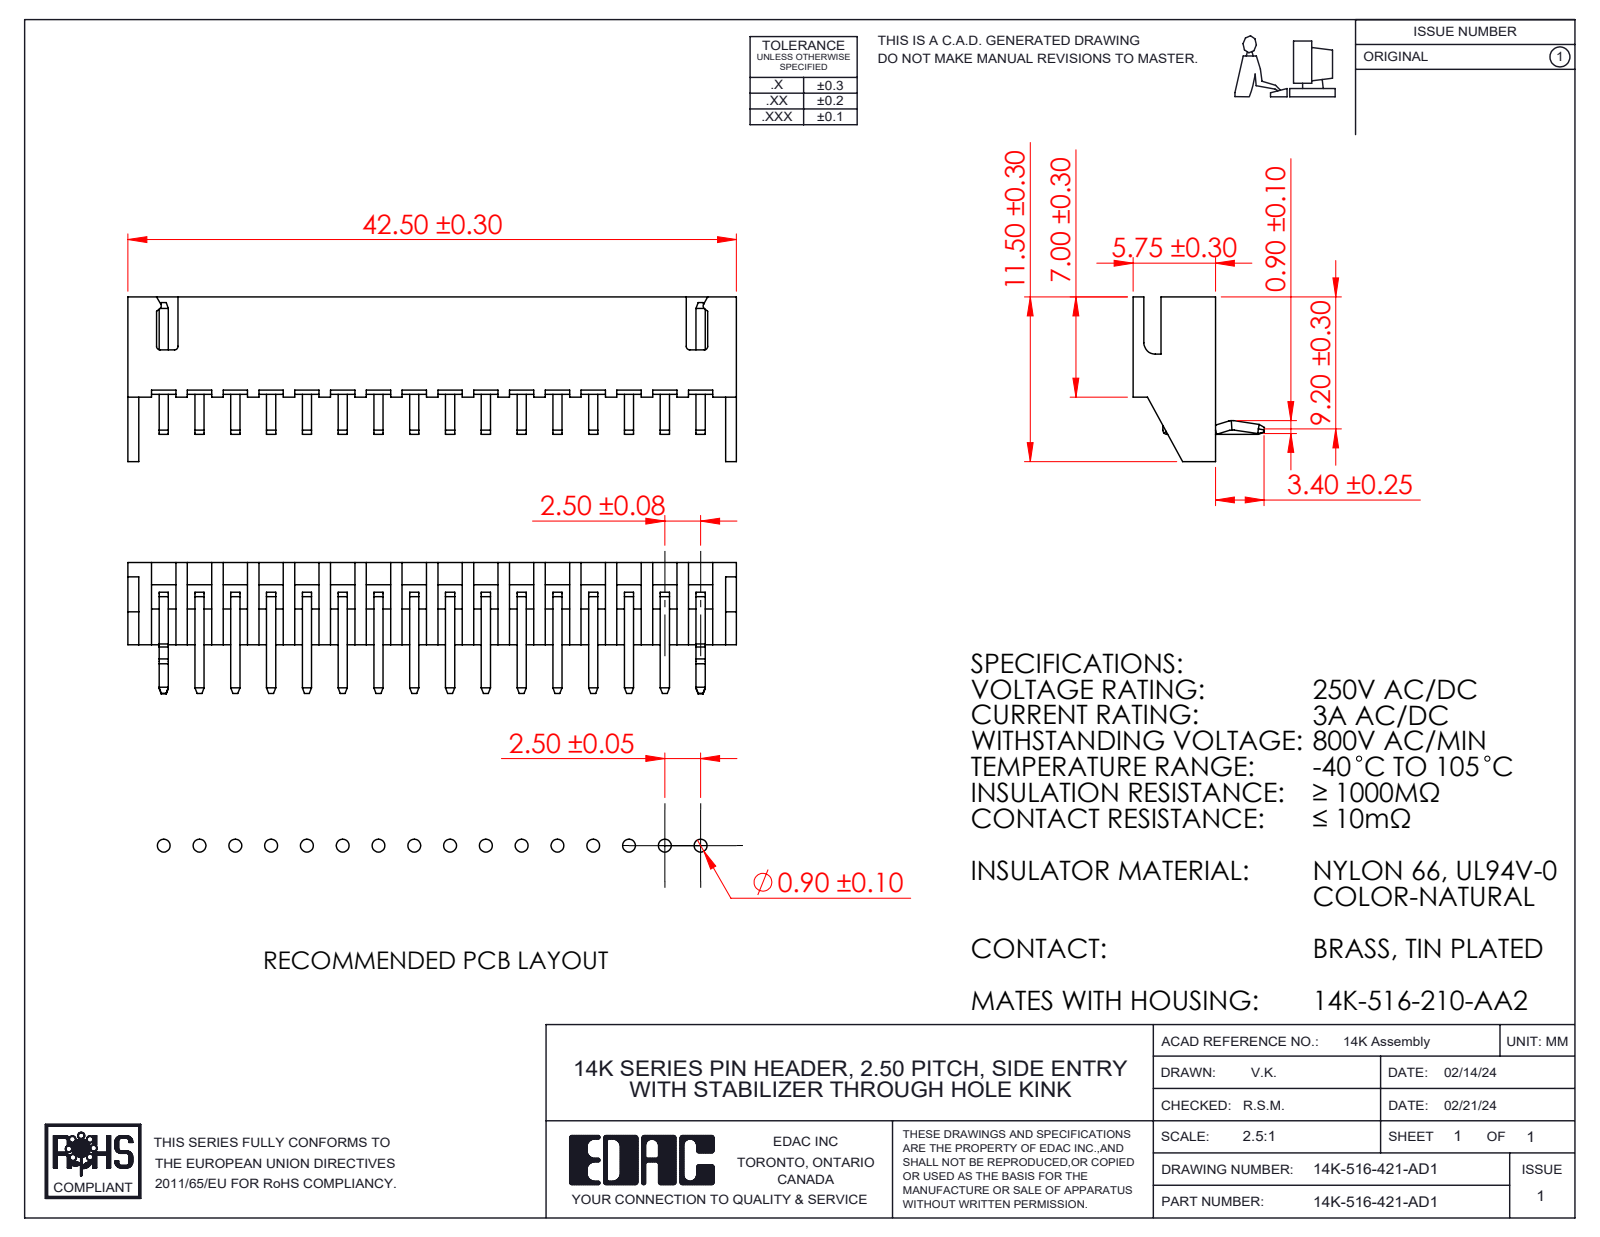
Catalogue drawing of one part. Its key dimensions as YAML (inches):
part_name: "14K Series Pin with Stabilizer_16; 14K Series Pin Header Insulator with Stabilizer_516; 14K-516-421-AD1; 14K Series Pin with Stabilizer_21"
step_written_by: "SolidWorks 2023 (CONFIG_CONTROL_DESIGN)"
units: inches
bodies: {solids: 17, faces: 586, planar: 533, cylindrical: 53, other: 0}
overall_size: [1.673, 0.453, 0.361]
volume: 0.051
surface_area: 3.765
partial_cylinders:
  - {radius: 0.01, count: 6}
  - {radius: 0.031, count: 4}
  - {radius: 0.012, count: 2}
  - {radius: 0.031, count: 1}
face_to_face_distances: [0.197, 0.03, 0.227, 0.167, 0.025, 0.077, 0.098, 0.295, 0.394, 0.12]
